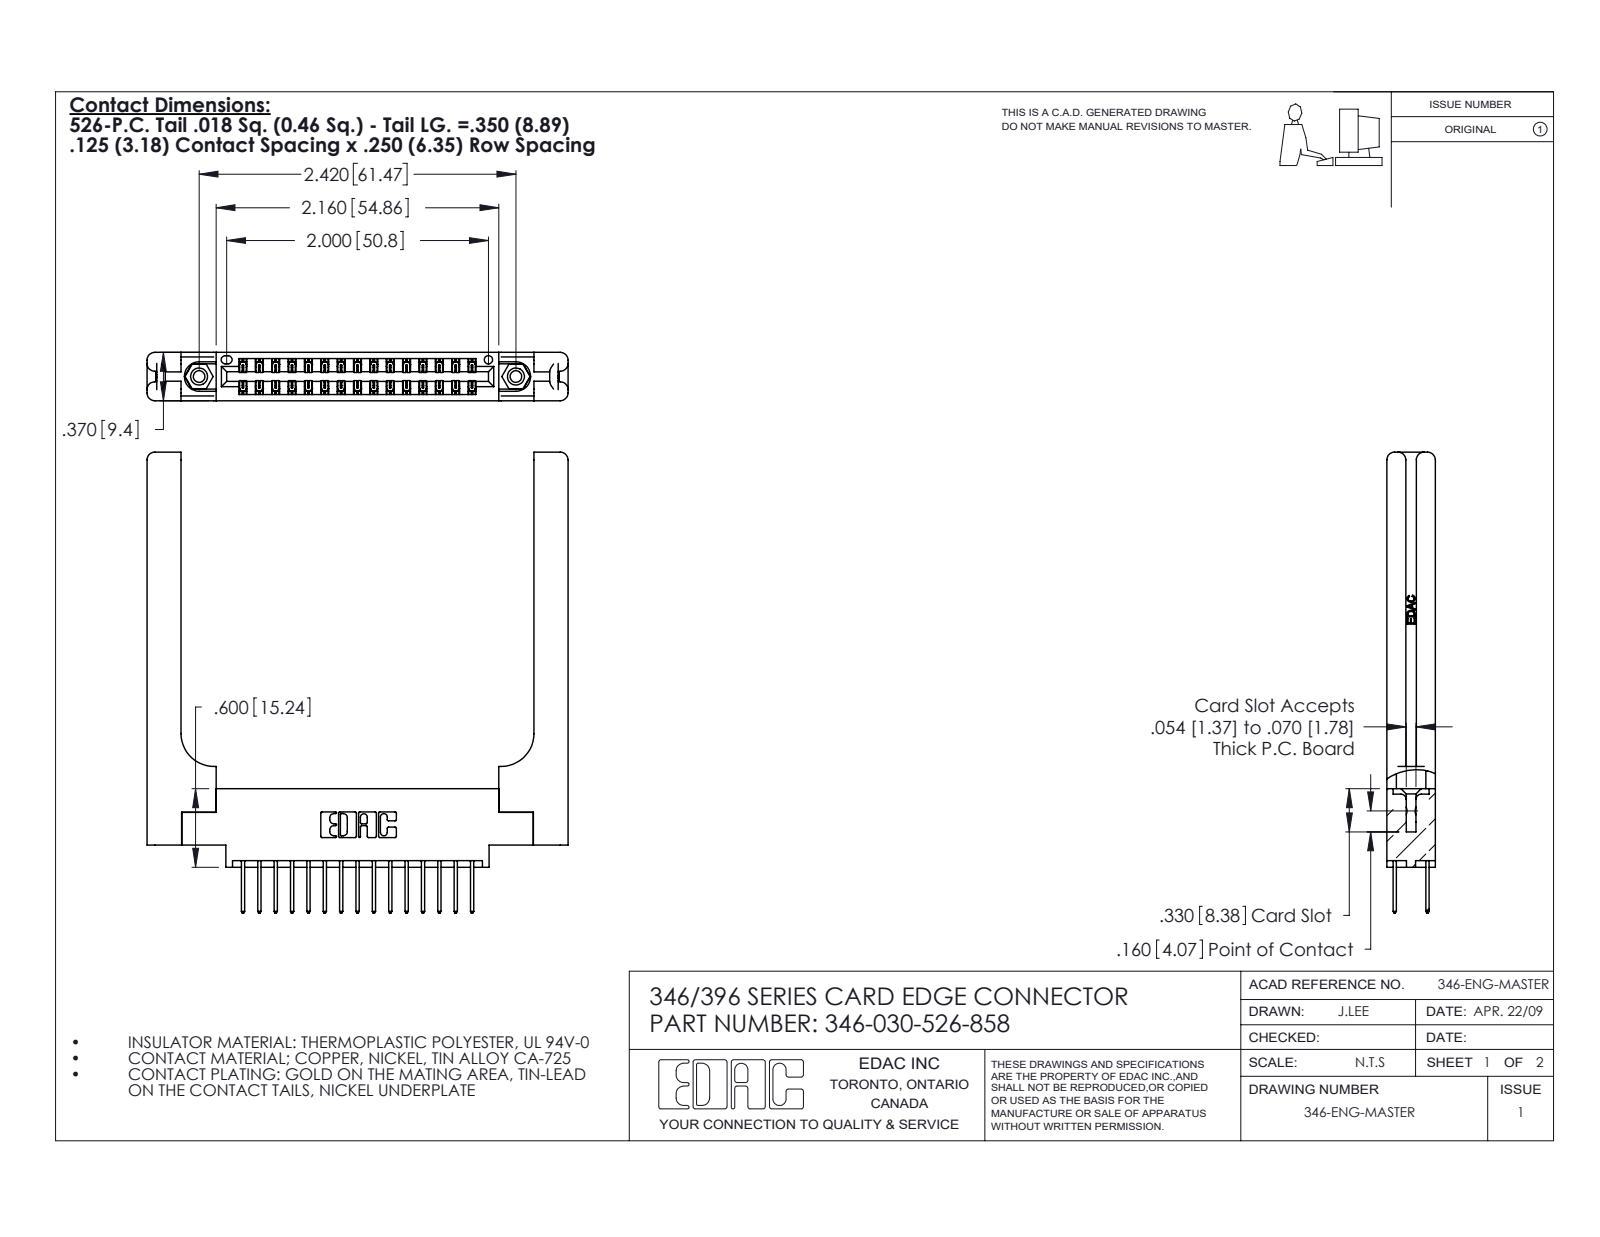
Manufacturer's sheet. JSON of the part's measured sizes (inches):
{"part_name": "346-220-058_345-220-058; 345-292-001_345-293-126; 346 Part_0.170 Offset - 0.156 Dia-TH; 345-250-001_345-250-001-102 (+1 more)", "step_written_by": "SolidWorks 2020 (CONFIG_CONTROL_DESIGN)", "units": "inches", "bodies": {"solids": 35, "faces": 1956, "planar": 1292, "cylindrical": 604, "other": 60}, "overall_size": [3.52, 3.216, 0.37], "volume_in3": 0.923, "surface_area_in2": 23.98, "round_holes": [[0.089, 2], [0.125, 2], [0.156, 2], [0.064, 1]], "round_bosses_or_shafts": [[0.155, 2]], "partial_cylinders_radius": [[0.006, 45], [0.01, 30], [0.01, 22], [0.06, 16], [0.007, 6], [0.031, 6], [0.026, 3], [0.014, 2]], "face_to_face_distances": [0.37, 0.072, 0.148, 0.15, 0.048, 0.322, 0.25, 0.077, 0.025, 0.298], "hole_center_spacings": [0.246, 2.213, 2.42]}
